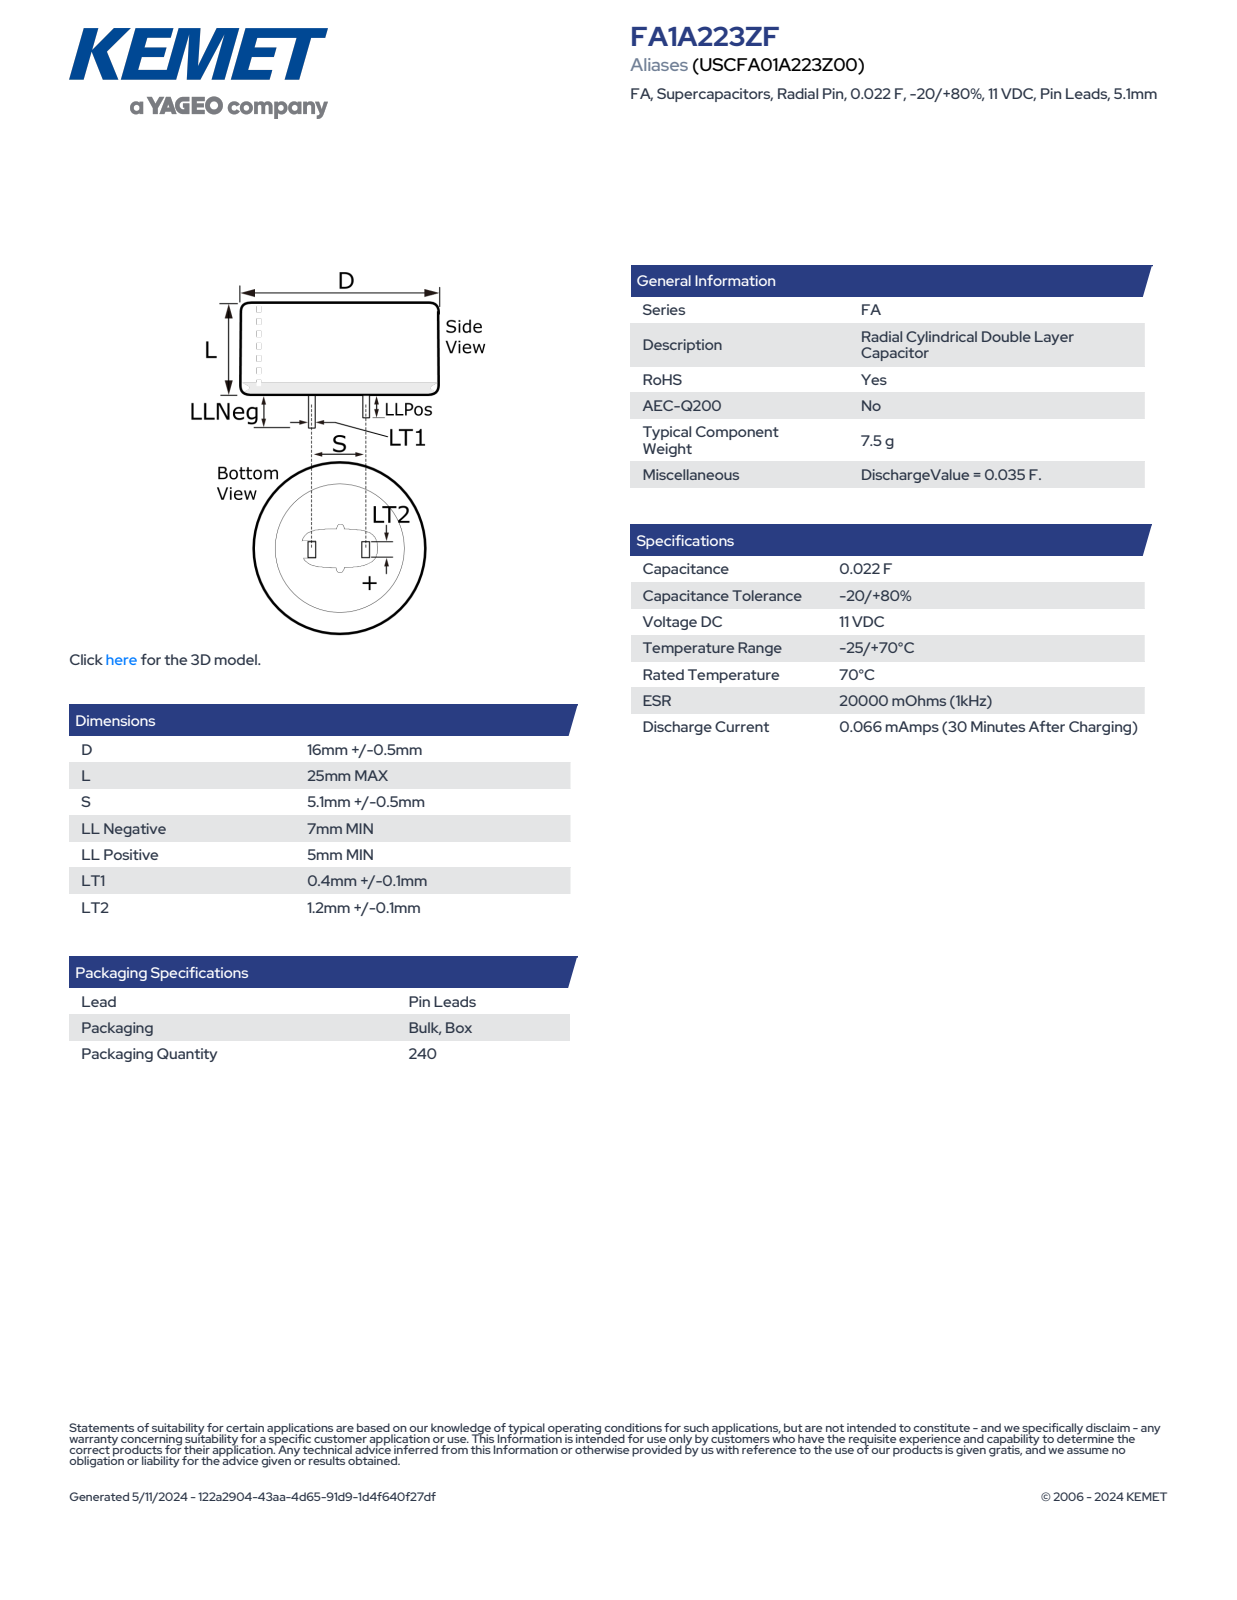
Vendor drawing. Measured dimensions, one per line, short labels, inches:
name: CDR_LPLLN_D16.5L25S5.1LLNEG7LLPOS5LT10.5LT21.3
written by: SolidWorks 2014 (AUTOMOTIVE_DESIGN)
unit: in
bodies: 1 solid, 78 faces (70 planar, 4 cylindrical, 4 other)
size: 1.26 × 0.65 × 0.65
volume: 0.323 in³; area: 2.626 in²
bosses: 1× ⌀0.65
rounds: 1× R0.325
face distances: 0.984, 0.02, 0.201, 0.22, 0.181, 0.051, 0.079, 0.276, 1.26, 0.197
